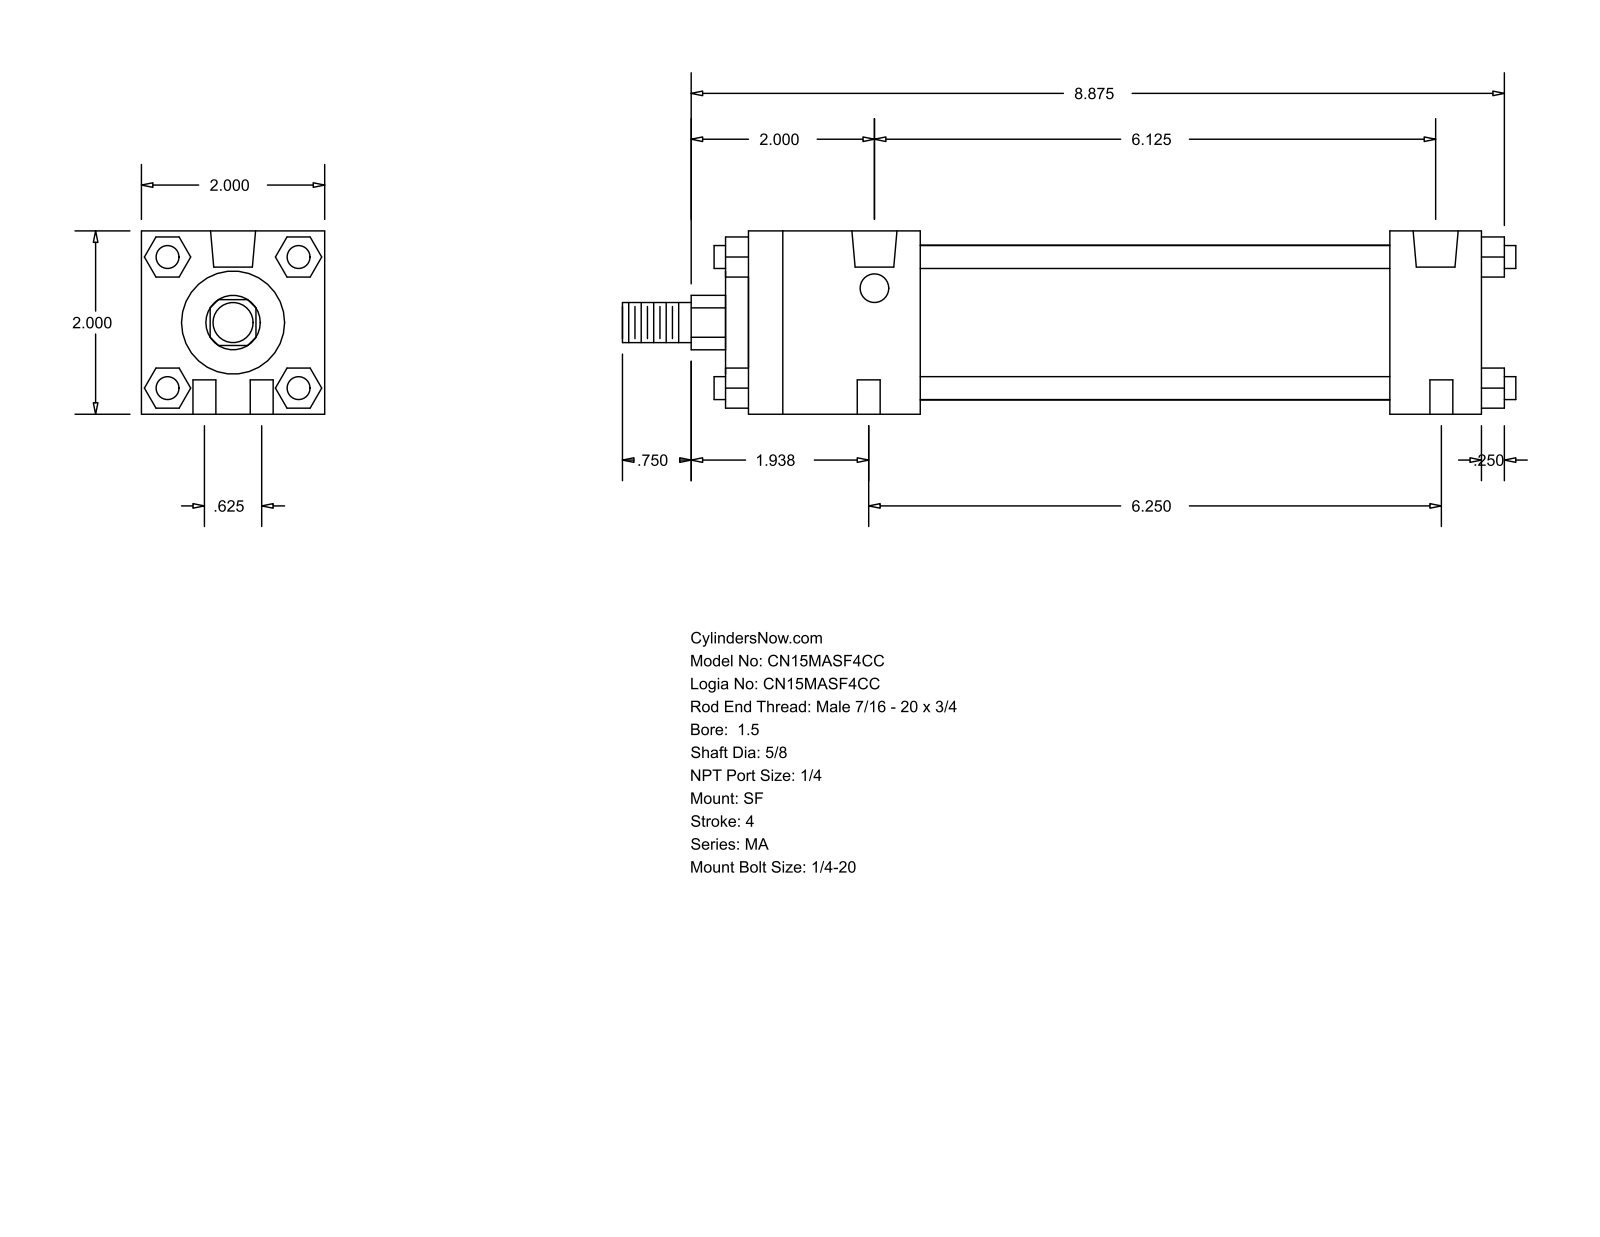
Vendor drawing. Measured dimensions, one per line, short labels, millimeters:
name: MA_SF__0150_0.625
written by: GSSL Pune (CONFIG_CONTROL_DESIGN)
unit: mm
bodies: 0 solids, 124 faces (94 planar, 30 cylindrical, 0 other)
size: 247.65 × 50.8 × 50.8
holes: 4× ⌀6.35, 2× ⌀7.94, 2× ⌀12.49
bosses: 4× ⌀6.35, 1× ⌀42.93, 1× ⌀28.57, 1× ⌀15.88, 1× ⌀11.11
rounds: 1× R7.54
face distances: 50.8, 203.19, 47.62, 177.8, 130.18, 155.57, 25.39, 6.35, 53.97, 184.15
hole spacings: 8.1, 15.88, 155.58, 157.36, 157.37, 158.75, 159.54
